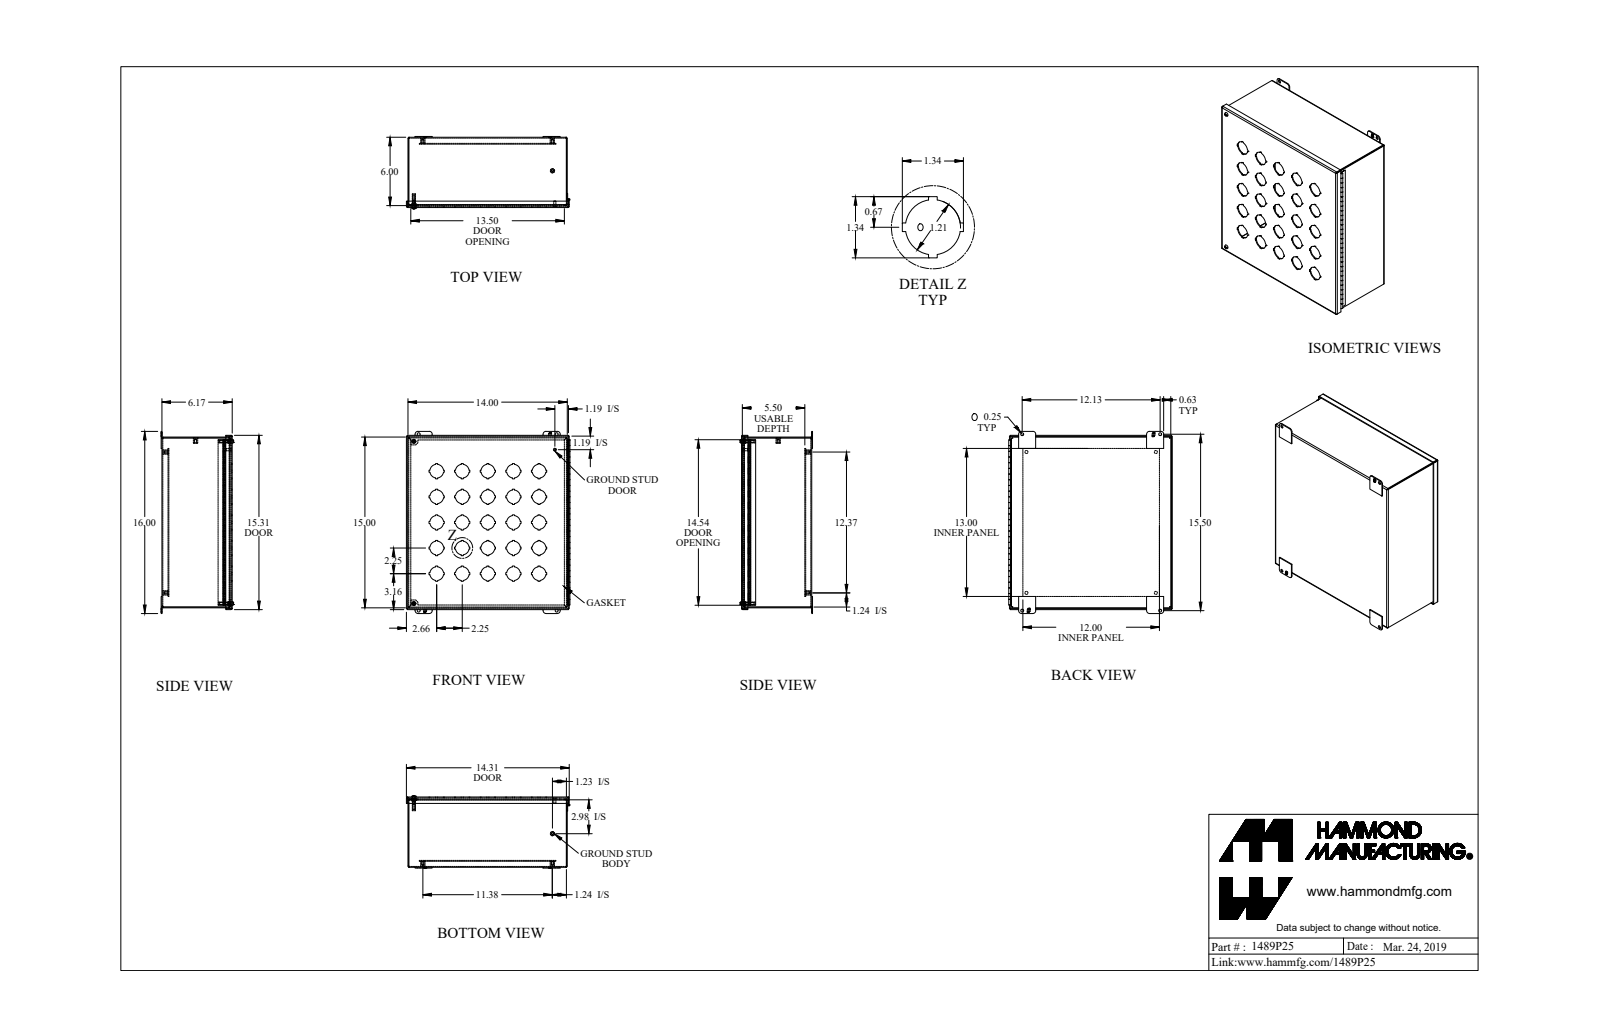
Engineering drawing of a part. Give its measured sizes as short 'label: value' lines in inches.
name: 1489P25_Default
written by: SolidWorks 2019 (CONFIG_CONTROL_DESIGN)
unit: in
bodies: 21 solids, 1167 faces (814 planar, 295 cylindrical, 58 other)
size: 16 × 14.373 × 6.371
volume: 76.54 in³; area: 2 058 in²
holes: 25× ⌀1.21, 6× ⌀0.25, 5× ⌀0.156, 4× ⌀0.265, 2× ⌀0.159, 2× ⌀0.406
bosses: 5× ⌀0.375, 2× ⌀0.39, 2× ⌀0.275, 2× ⌀0.19, 2× ⌀0.148, 1× ⌀0.25, 1× ⌀0.188, 1× ⌀0.174
rounds: 12× R0.036, 12× R0.108, 8× R0.25, 2× R0.16, 2× R0.171, 1× R0.125
face distances: 0.072, 6.1, 5.568, 0.532, 6.028, 6.172, 13.928, 0.604, 14.928, 5.64
hole spacings: 5.031, 2.25, 3.182, 7.115, 4.5, 8.113, 6.75, 6.364
